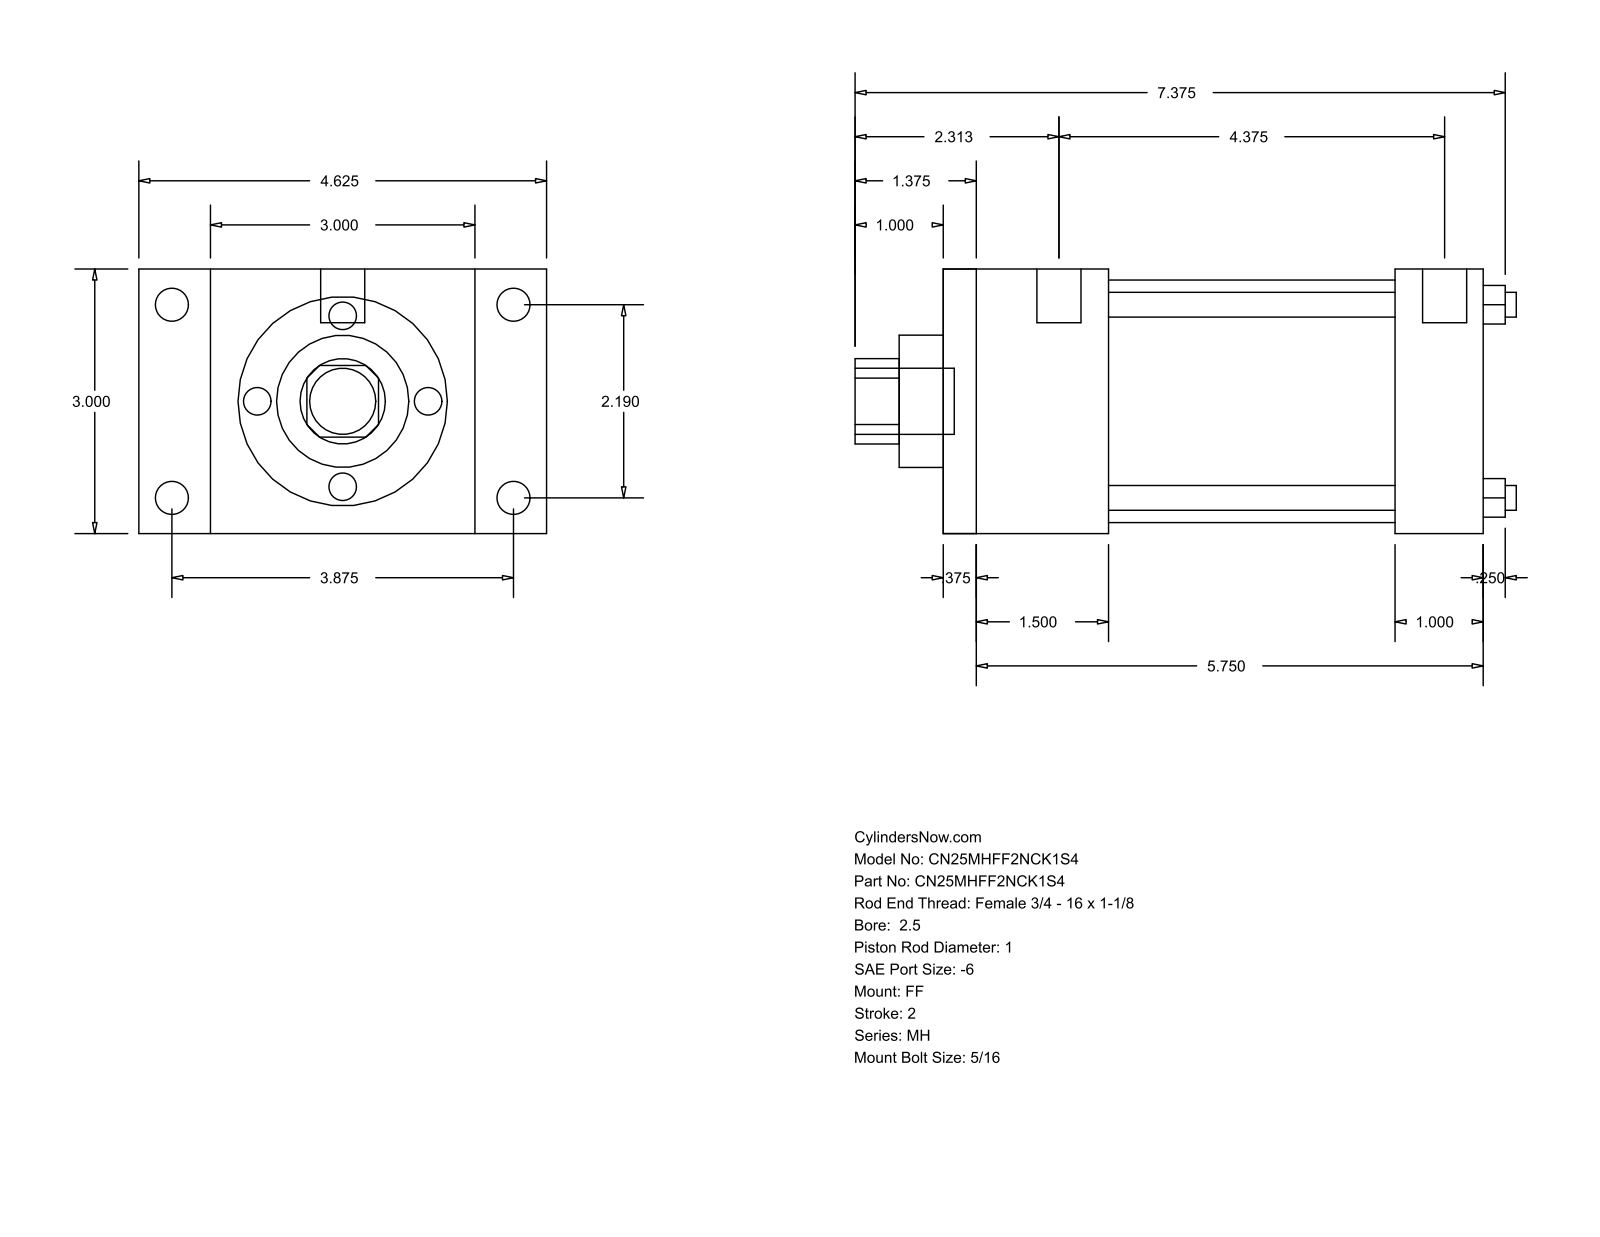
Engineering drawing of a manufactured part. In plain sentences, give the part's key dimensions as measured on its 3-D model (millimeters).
The part is named "MH_FF__0250_1". Its 3-D file was written by "GSSL Pune (CONFIG_CONTROL_DESIGN)". It is 0 solids with 92 faces: 64 planar, 28 cylindrical and 0 other. Overall it measures 190.5 by 117.47 by 76.2 millimeters. Round holes: 4 of diameter 7.14, 1 of diameter 25.4, 1 of diameter 38.1, 1 of diameter 69.85. Round bosses or shafts: 4 of diameter 9.53, 4 of diameter 5.56, 2 of diameter 12.7, 1 of diameter 19.05. Partial cylindrical surfaces (rounded edges, fillets, slot ends): 1 of radius 12.29. The main face-to-face distances are 76.2, 155.57, 9.52, 146.05, 25.4, 47.63, 130.17, 38.11, 120.65, 82.54. The hole center spacings are 39.33, 55.62, 78.66.
